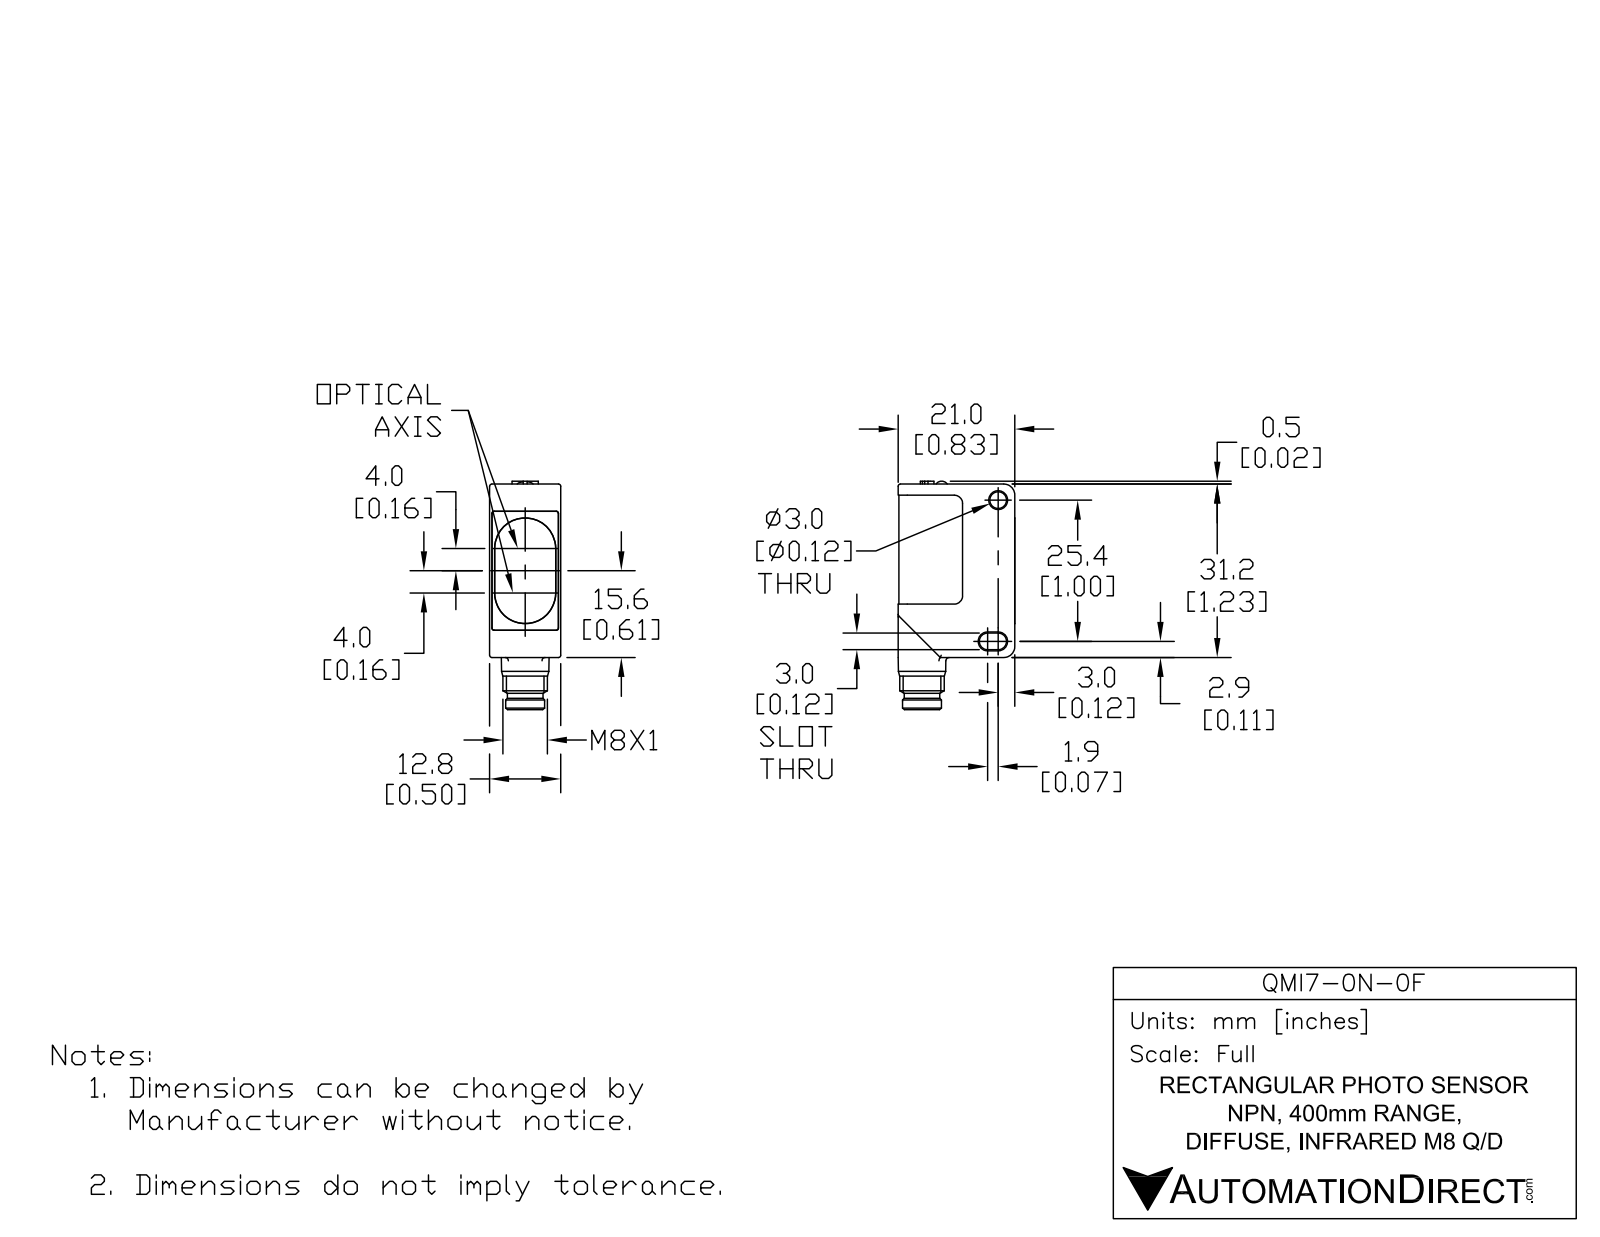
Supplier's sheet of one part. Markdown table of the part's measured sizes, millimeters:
| quantity | value |
| --- | --- |
| part name | QMI7-0N-0F |
| STEP written by | SolidWorks 2017 (AUTOMOTIVE_DESIGN) |
| units | millimeters |
| bodies | 7 solids, 272 faces (125 planar, 100 cylindrical, 47 other) |
| overall size | 41.1 × 21 × 12.8 |
| volume | 7 770 mm³ |
| surface area | 4 999 mm² |
| round holes (diameter × count) | 3 × 3, 5.8 × 1 |
| round bosses / shafts (diameter × count) | 1 × 4, 3.5 × 2, 8 × 1, 7 × 1, 6.4 × 1 |
| partial cylindrical surfaces (radius × count) | 0.4 × 10, 0.5 × 9, 1.5 × 6, 0.6 × 4, 1 × 4, 0.2 × 2, 1.1 × 2, 1.7 × 2 |
| main face-to-face distances | 12.6, 0.5, 12.8, 2.8, 0.4, 12.5, 12.4, 12.2, 1.5, 18.1 |
| hole center spacings | 1, 5.2, 6.2 |
